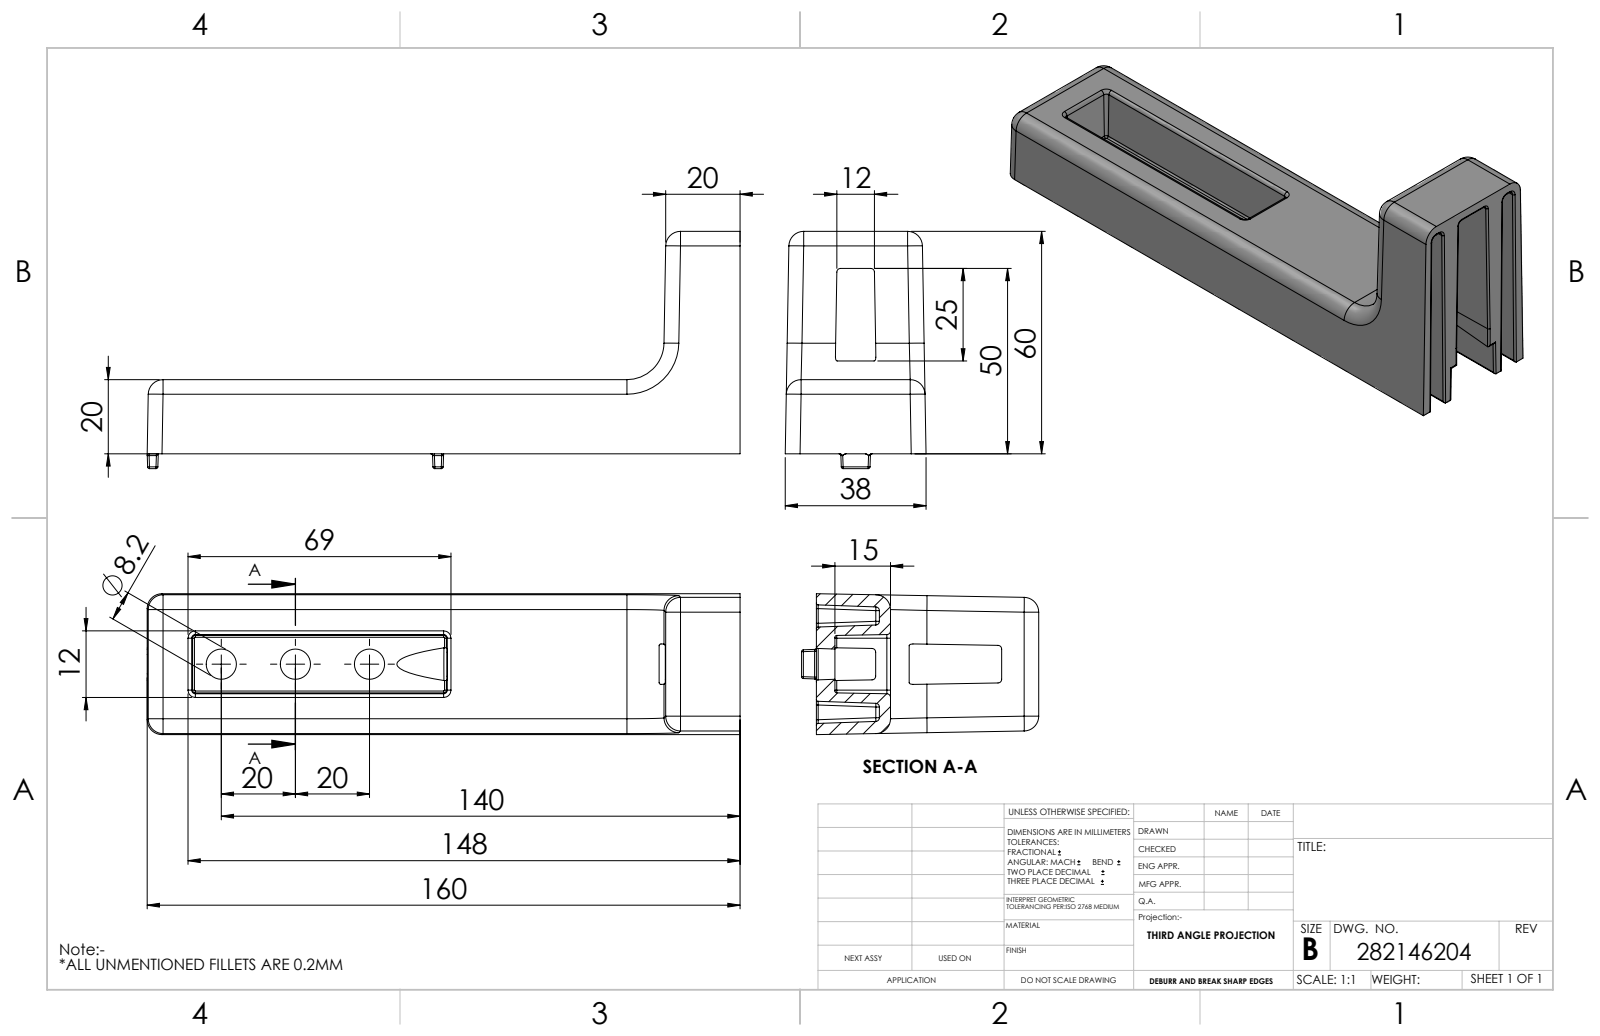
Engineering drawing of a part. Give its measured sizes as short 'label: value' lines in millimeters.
name: 282146204 Bodenwinkel 160x60x38
written by: Autodesk Inventor 2016 (AUTOMOTIVE_DESIGN)
unit: mm
bodies: 1 solid, 429 faces (89 planar, 199 cylindrical, 141 other)
size: 160.01 × 64 × 38
volume: 73 211 mm³; area: 41 737 mm²
rounds: 81× R0.5, 66× R1, 10× R4, 4× R1.5, 1× R8, 1× R10
face distances: 20, 10.75, 25.97, 1, 15.91, 26.66, 27, 26.97, 3, 12
